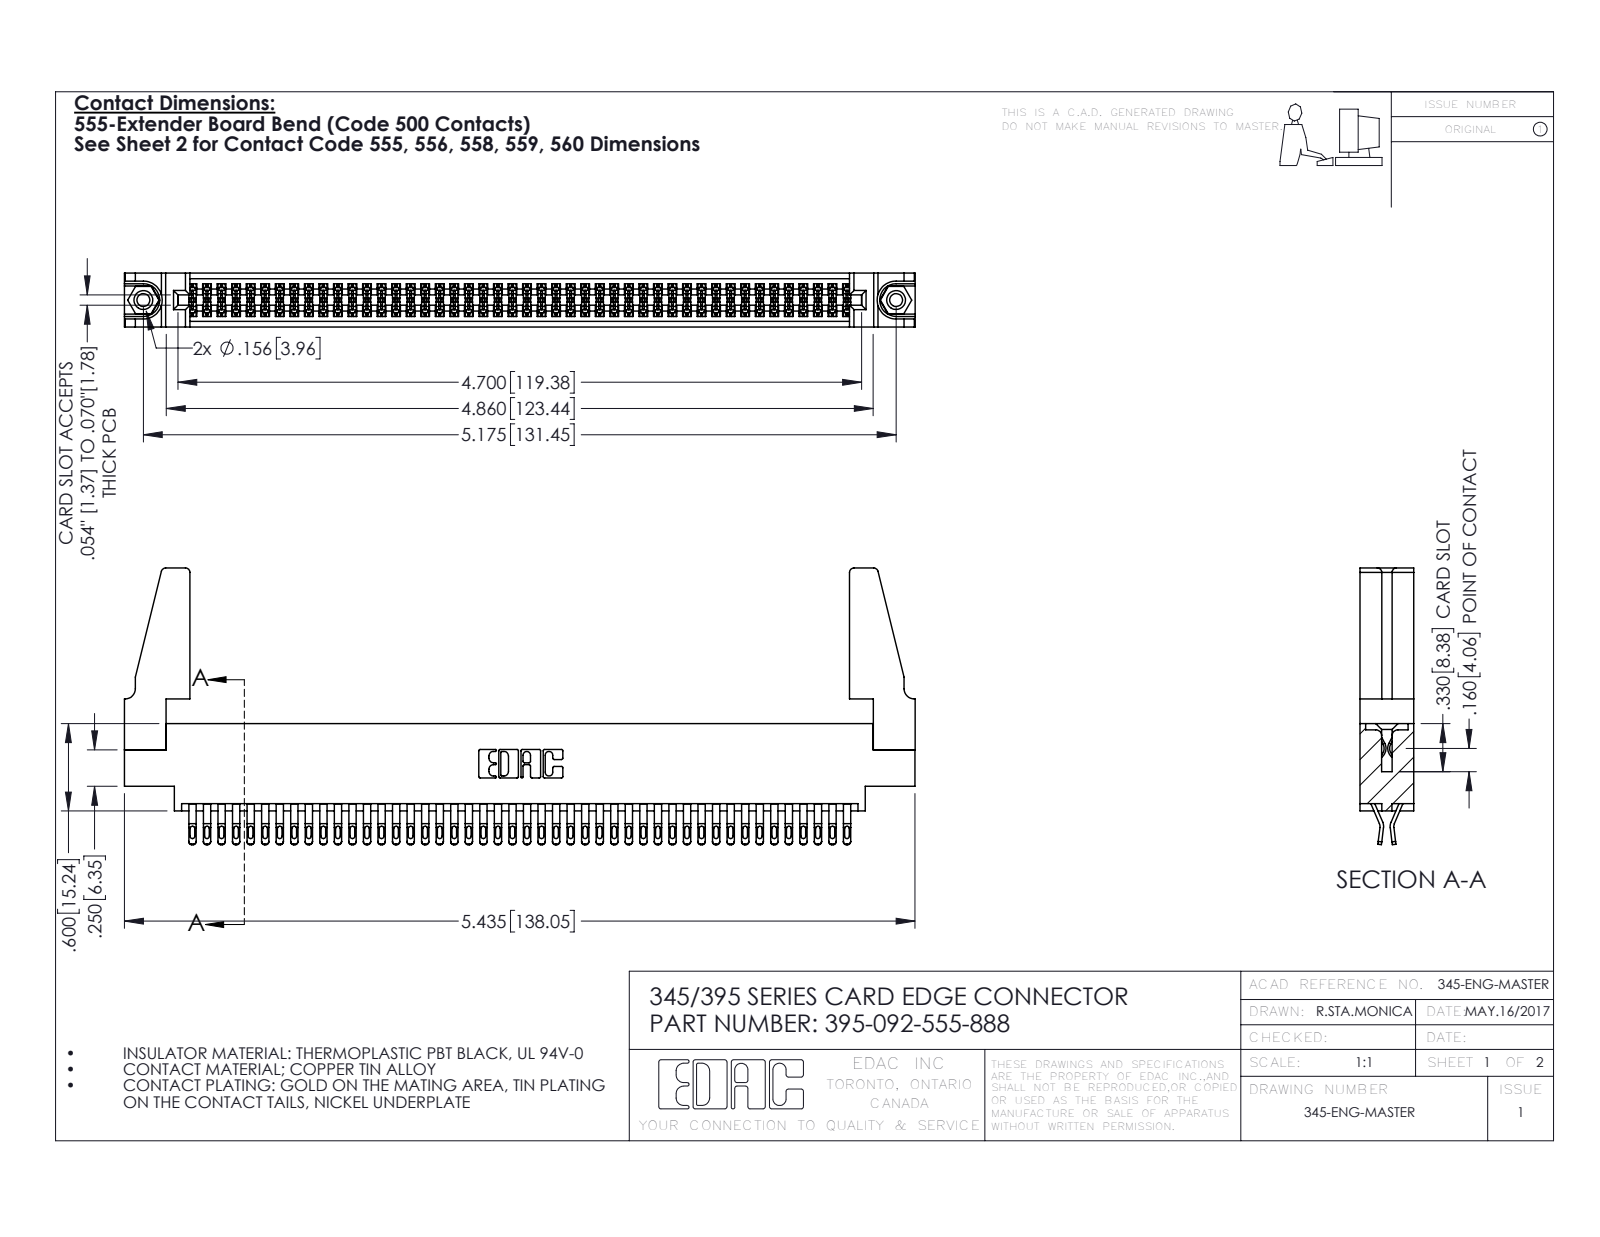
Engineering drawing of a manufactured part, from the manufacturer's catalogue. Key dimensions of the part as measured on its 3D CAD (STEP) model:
Part name (STEP PRODUCT): 345-220-078_345-220-088; 345 Part_0.170 Offset - 0.156 Dia-TH; 345-250-001_345-250-001-102; 345-292-001_555 Tail (+1 more)
STEP written by: SolidWorks 2016 (CONFIG_CONTROL_DESIGN)
Units: inches
Bodies: 97 solids, 5406 faces (3008 planar, 2382 cylindrical, 16 other)
Overall size (bounding box): 5.436 × 1.902 × 0.37
Volume: 1.029 in³ · Surface area: 37.79 in²
Round holes (diameter × count): ⌀0.089 ×2, ⌀0.125 ×2, ⌀0.156 ×2, ⌀0.064 ×1
Round bosses / shafts (diameter × count): ⌀0.155 ×2
Partial cylindrical surfaces — rounded edges, fillets, slot ends (radius × count): R0.016 ×230, R0.02 ×184, R0.006 ×138, R0.01 ×22, R0.03 ×8, R0.007 ×6, R0.031 ×6, R0.026 ×3
Main face-to-face distances: 0.072, 0.298, 0.37, 0.025, 0.2, 0.098, 0.272, 0.225, 0.175, 0.149
Hole centre spacings: 0.27, 4.939, 5.175
